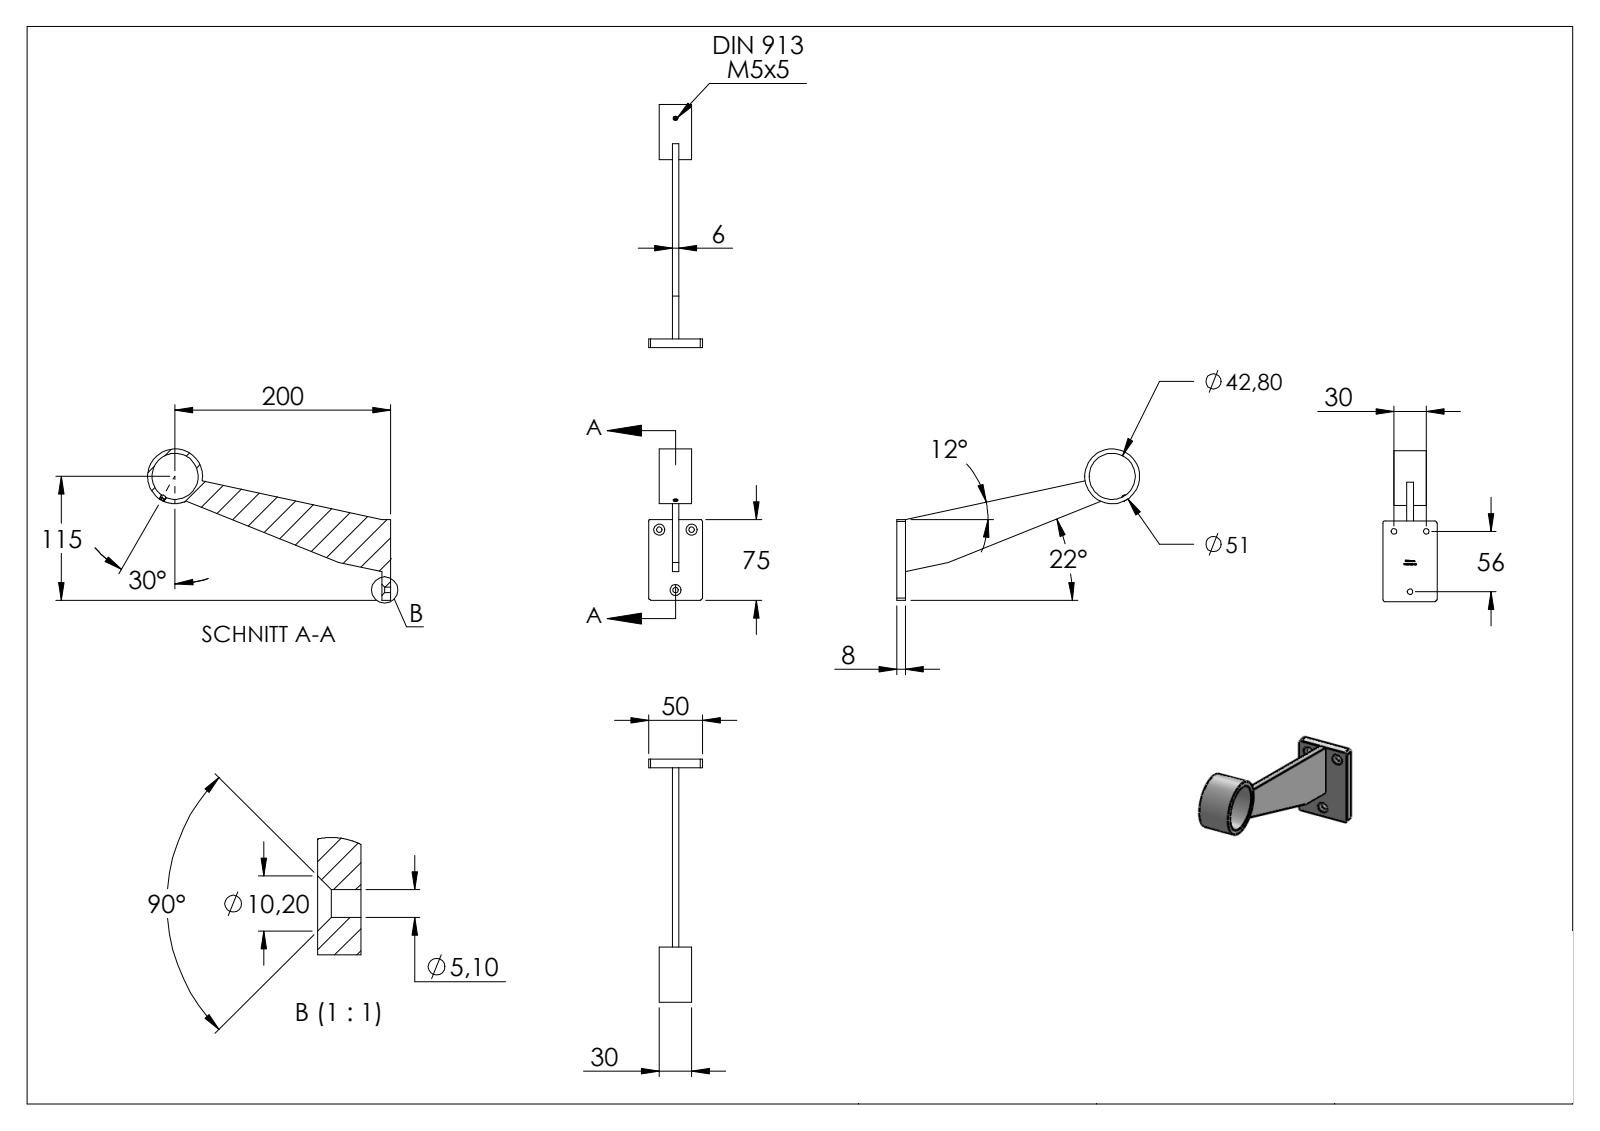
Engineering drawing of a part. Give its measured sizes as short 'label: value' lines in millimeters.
name: DIN913 M5x5_DIN913 M5x5; 70022-240-42 Teil1_70022-240-42 Teil1; 70022-240-42
written by: SolidWorks 2018 (CONFIG_CONTROL_DESIGN)
unit: mm
bodies: 2 solids, 283 faces (168 planar, 11 cylindrical, 104 other)
size: 225.5 × 140.5 × 50
volume: 87 790 mm³; area: 35 091 mm²
holes: 3× ⌀5.1, 1× ⌀4.2, 1× ⌀42.8
bosses: 1× ⌀51, 1× ⌀5
rounds: 4× R2
face distances: 6, 8, 12, 18, 10, 22, 28, 40, 30, 50
hole spacings: 57.97, 30
